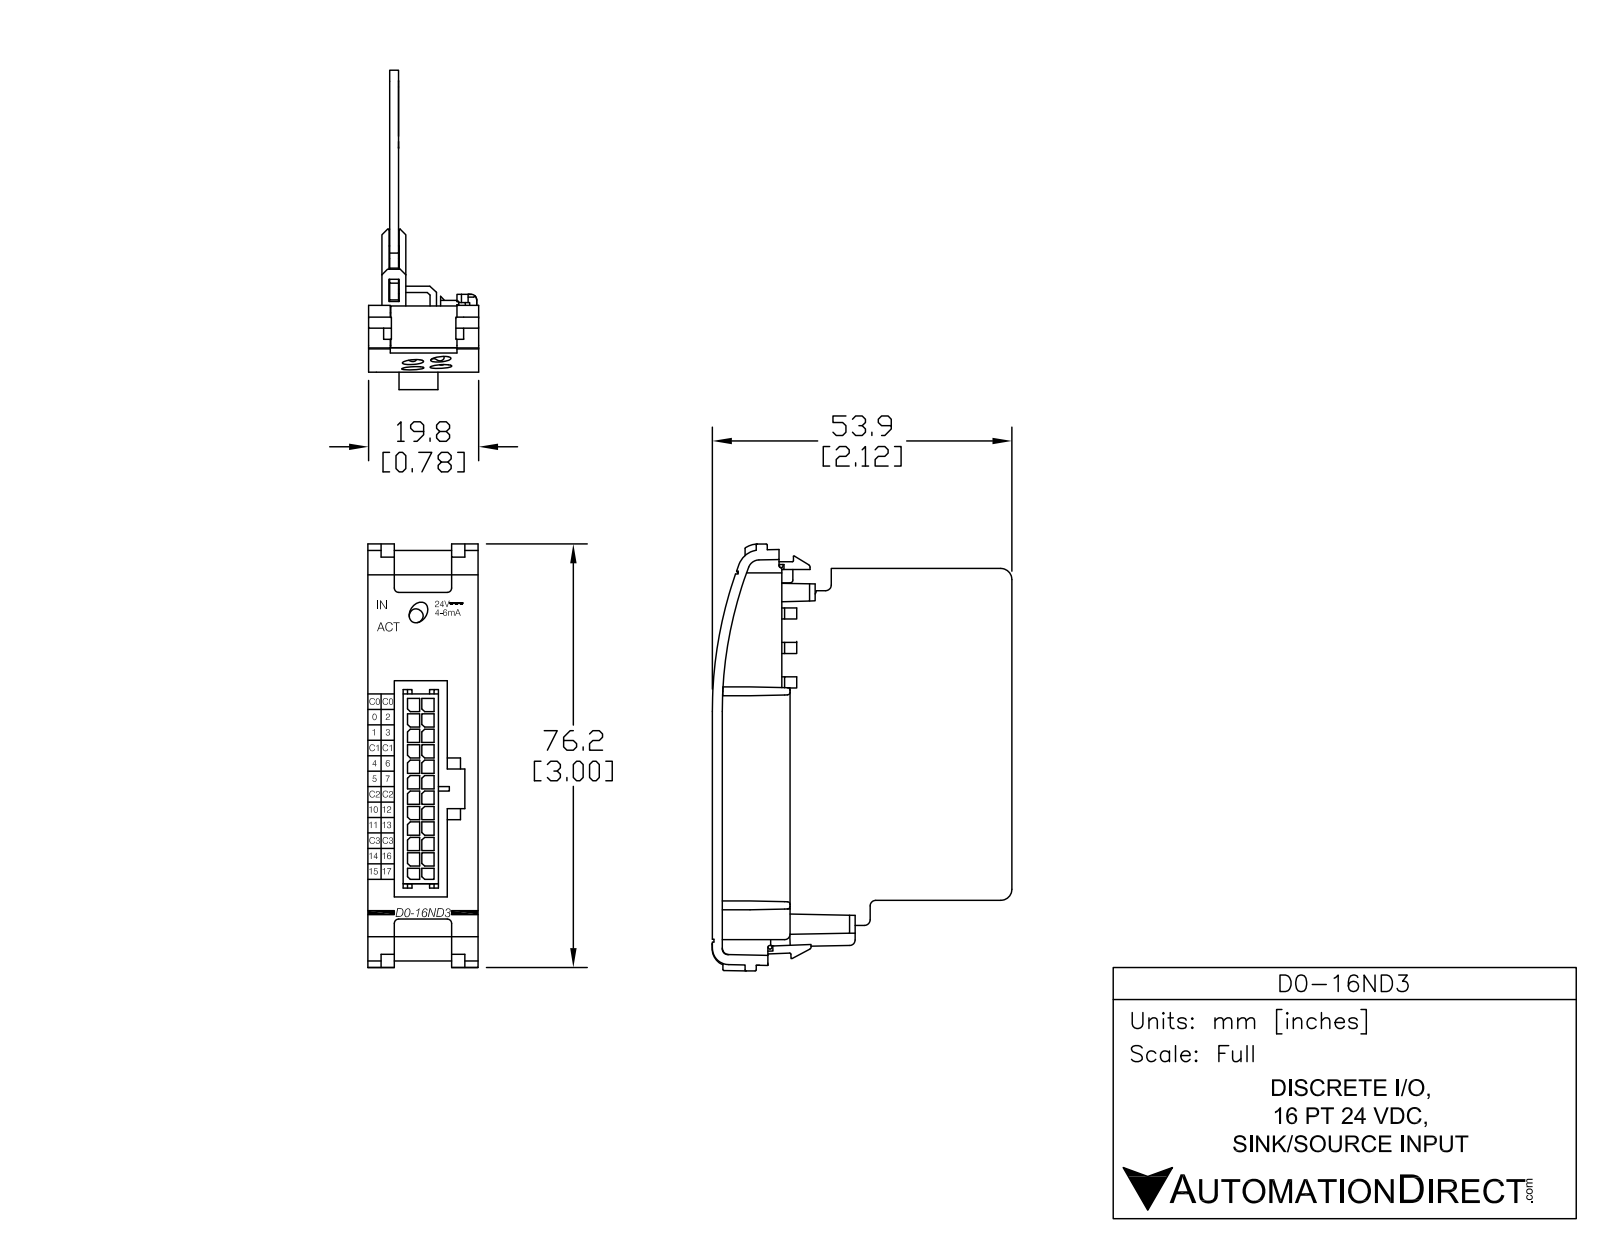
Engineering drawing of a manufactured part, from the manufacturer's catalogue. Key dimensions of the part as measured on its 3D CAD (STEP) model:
Part name (STEP PRODUCT): D0-16ND3
STEP written by: SolidWorks 2009 (AUTOMOTIVE_DESIGN)
Units: inches
Bodies: 1 solid, 389 faces (302 planar, 38 cylindrical, 49 other)
Overall size (bounding box): 3.08 × 2.27 × 0.826
Volume: 0.625 in³ · Surface area: 22.06 in²
Partial cylindrical surfaces — rounded edges, fillets, slot ends (radius × count): R0.005 ×4, R0.02 ×3, R0.035 ×3, R0.025 ×2, R0.01 ×1, R0.04 ×1, R0.065 ×1, R0.07 ×1
Main face-to-face distances: 0.063, 0.05, 0.631, 0.075, 0.581, 0.113, 0.518, 0.681, 0.568, 0.015
